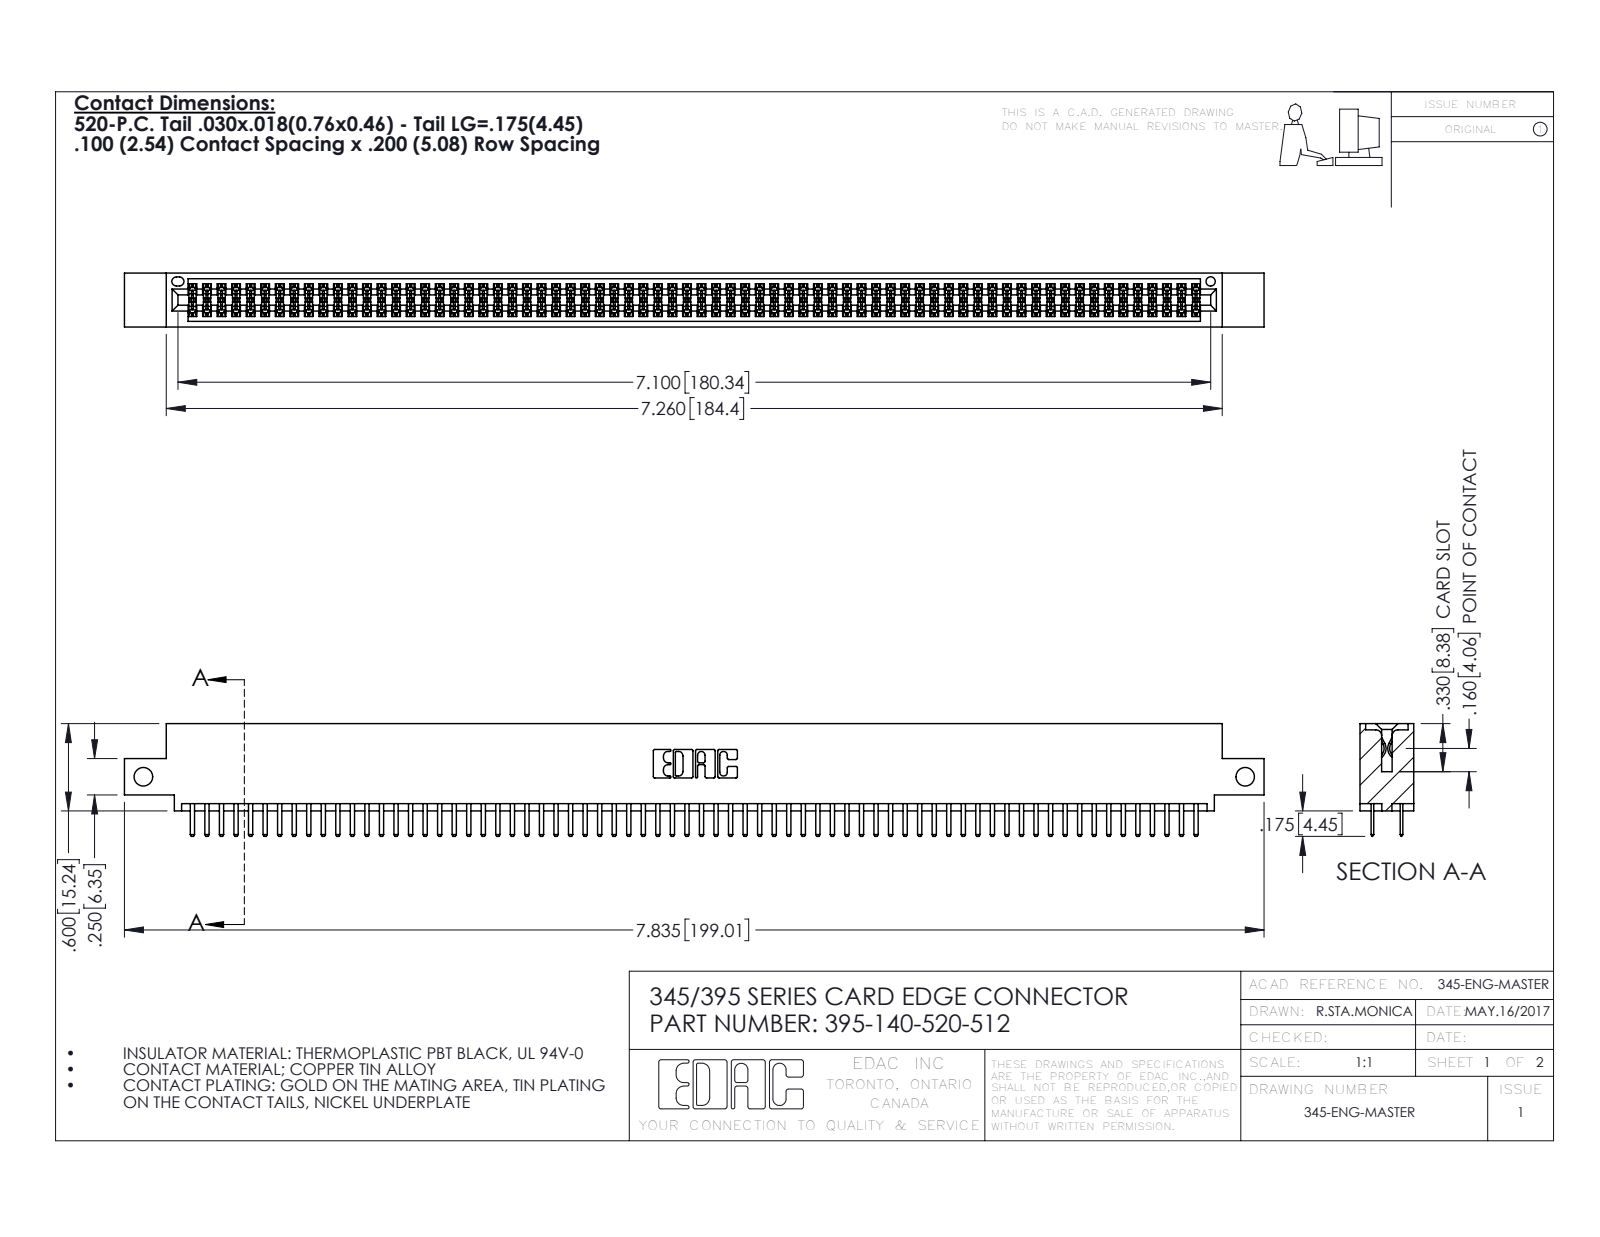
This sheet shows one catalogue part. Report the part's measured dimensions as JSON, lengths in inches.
{"part_name": "345 Part_0.110 Offset - Side Mount; 345-292-001_345-293-120; 395-140-520-512", "step_written_by": "SolidWorks 2016 (CONFIG_CONTROL_DESIGN)", "units": "inches", "bodies": {"solids": 141, "faces": 7690, "planar": 4984, "cylindrical": 2706, "other": 0}, "overall_size": [7.835, 0.775, 0.37], "volume_in3": 1.182, "surface_area_in2": 44.95, "round_holes": [[0.128, 2], [0.064, 1]], "partial_cylinders_radius": [[0.006, 210], [0.01, 144], [0.01, 22], [0.007, 6], [0.031, 6], [0.026, 3], [0.014, 2], [0.019, 2]], "face_to_face_distances": [0.298, 0.072, 0.2, 0.37, 0.098, 0.272, 0.025, 0.225, 0.022, 0.072], "hole_center_spacings": [7.575]}
